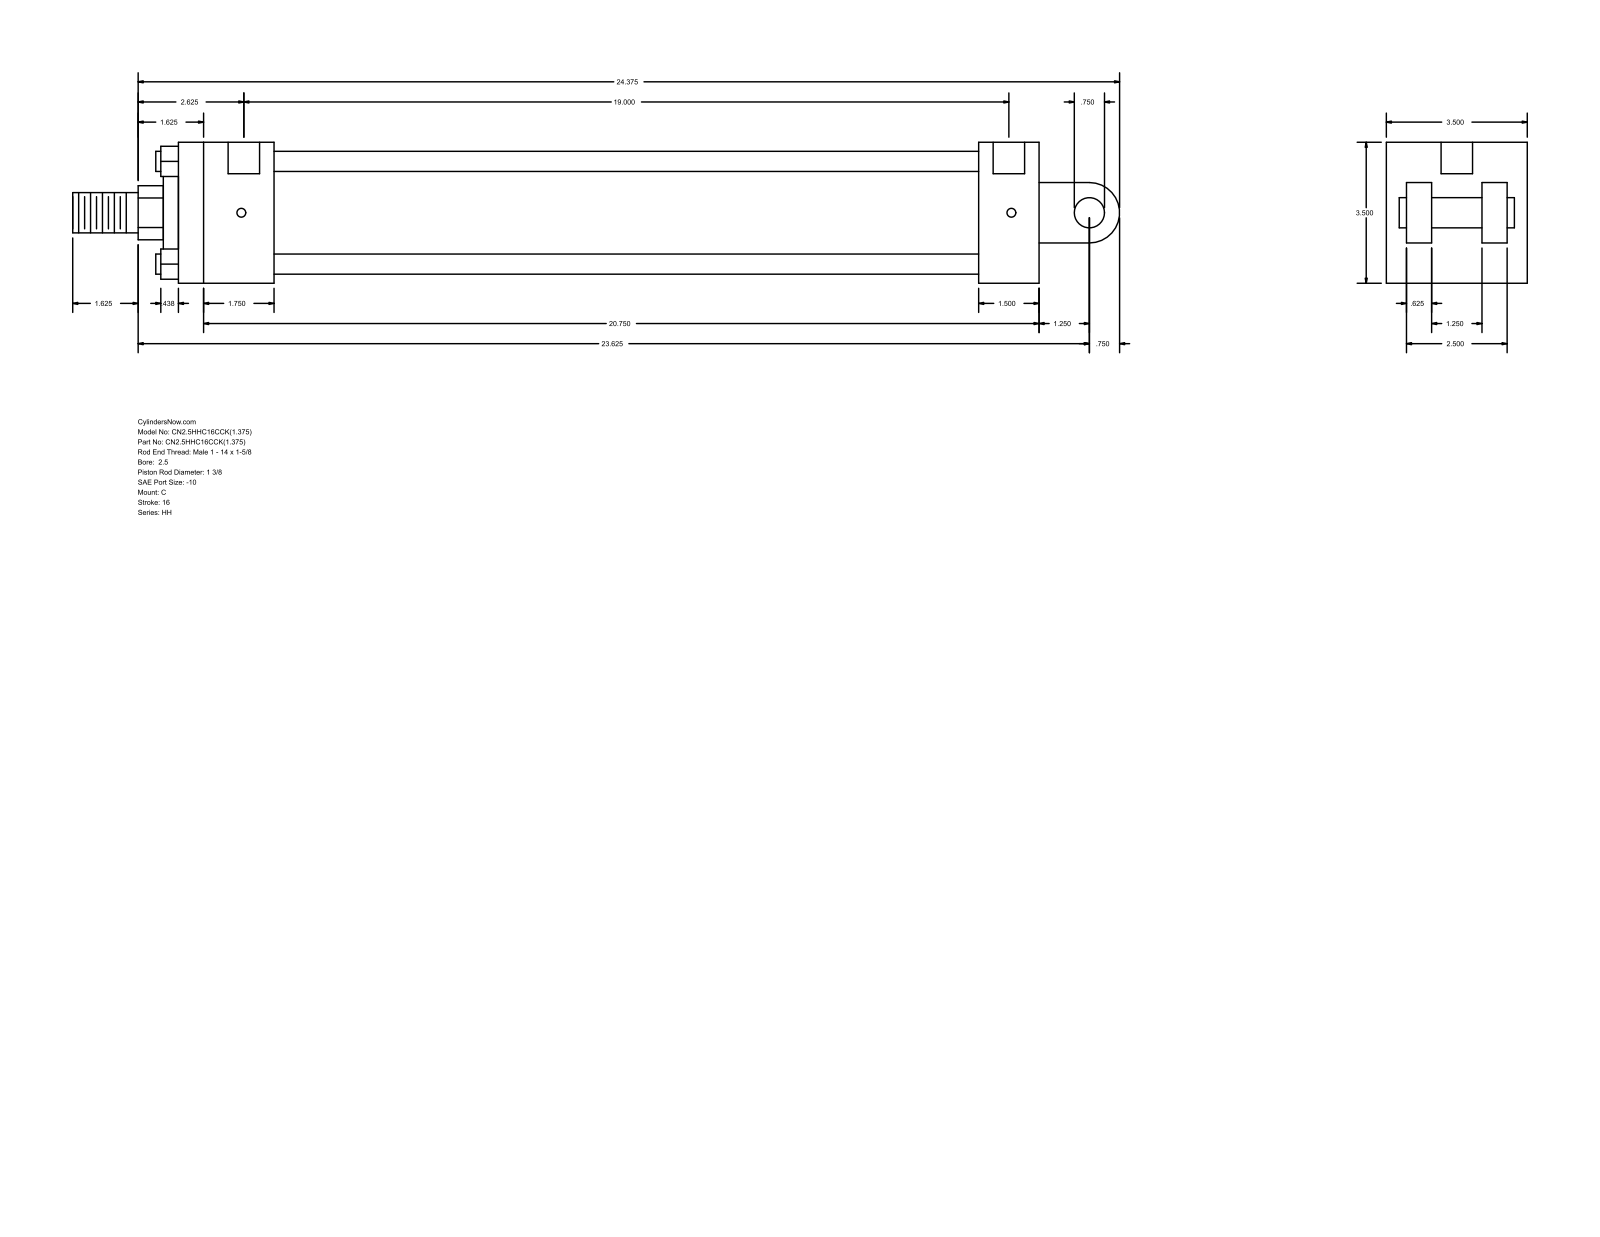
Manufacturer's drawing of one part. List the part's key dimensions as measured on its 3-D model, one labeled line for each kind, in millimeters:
Part name (STEP PRODUCT): HH_C__0250_1.375
STEP written by: GSSL Pune (CONFIG_CONTROL_DESIGN)
Units: millimetres
Bodies: 0 solids, 99 faces (70 planar, 29 cylindrical, 0 other)
Overall size (bounding box): 660.4 × 88.9 × 88.9
Round holes (diameter × count): ⌀5.56 ×4, ⌀19.84 ×2
Round bosses / shafts (diameter × count): ⌀12.7 ×4, ⌀73.03 ×1, ⌀50.8 ×1, ⌀34.92 ×1, ⌀25.4 ×1, ⌀19.05 ×1
Partial cylindrical surfaces — rounded edges, fillets, slot ends (radius × count): R17.06 ×1, R19.05 ×1
Main face-to-face distances: 88.9, 542.93, 38.1, 63.5, 12.7, 504.83, 60.32, 444.51, 482.61, 28.57
Hole centre spacings: 485.77, 1.58, 1.59, 482.6, 484.18, 484.19
